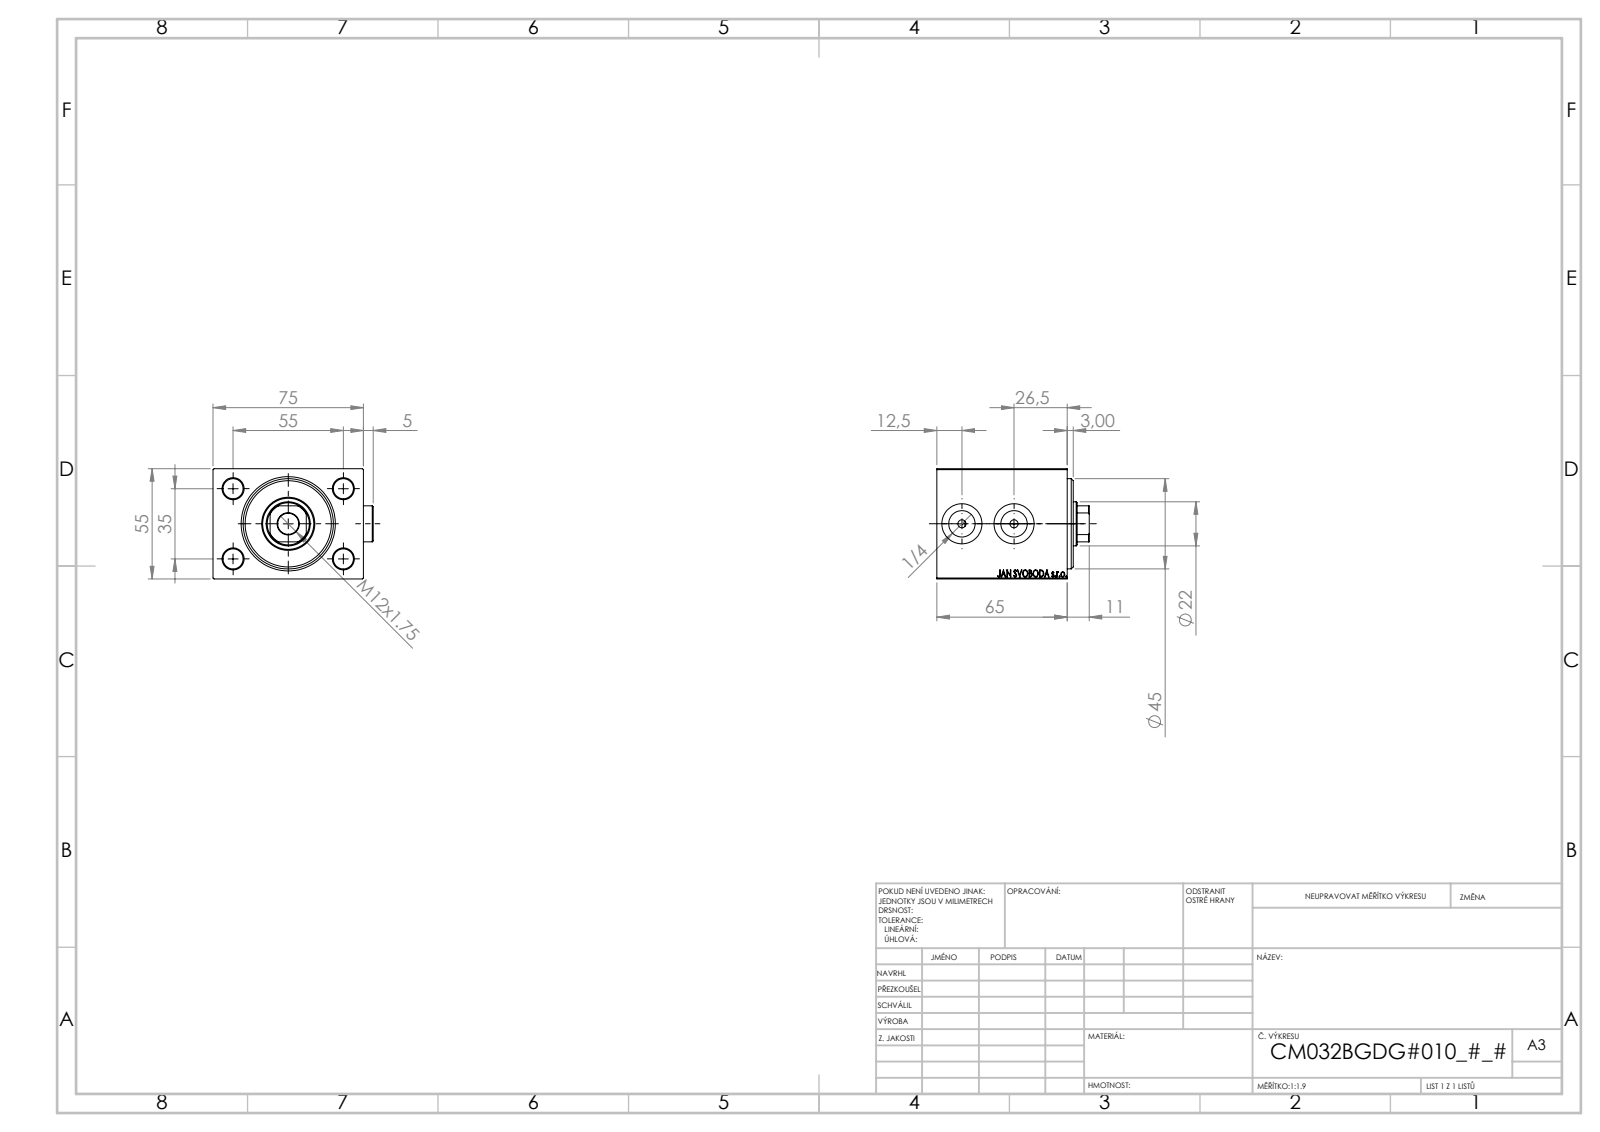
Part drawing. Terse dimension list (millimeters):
name: Zatka_OIL_PORT; V450CM_VC_B; V450CM_B_VCP; V450CM_B_Body
written by: SolidWorks 2019 (CONFIG_CONTROL_DESIGN)
unit: mm
bodies: 5 solids, 934 faces (436 planar, 68 cylindrical, 430 other)
size: 79.9 × 76 × 55
volume: 250 344 mm³; area: 54 026 mm²
holes: 4× ⌀10, 2× ⌀4, 2× ⌀13.16, 2× ⌀20, 1× ⌀10.5, 1× ⌀22, 1× ⌀25.5, 1× ⌀26.5, 1× ⌀32, 1× ⌀34, 1× ⌀45
bosses: 2× ⌀18
rounds: 1× R10.5
face distances: 55, 75, 65, 5, 51, 14, 46, 60, 74.9, 8
hole spacings: 32.6, 35, 55, 65.19, 26
